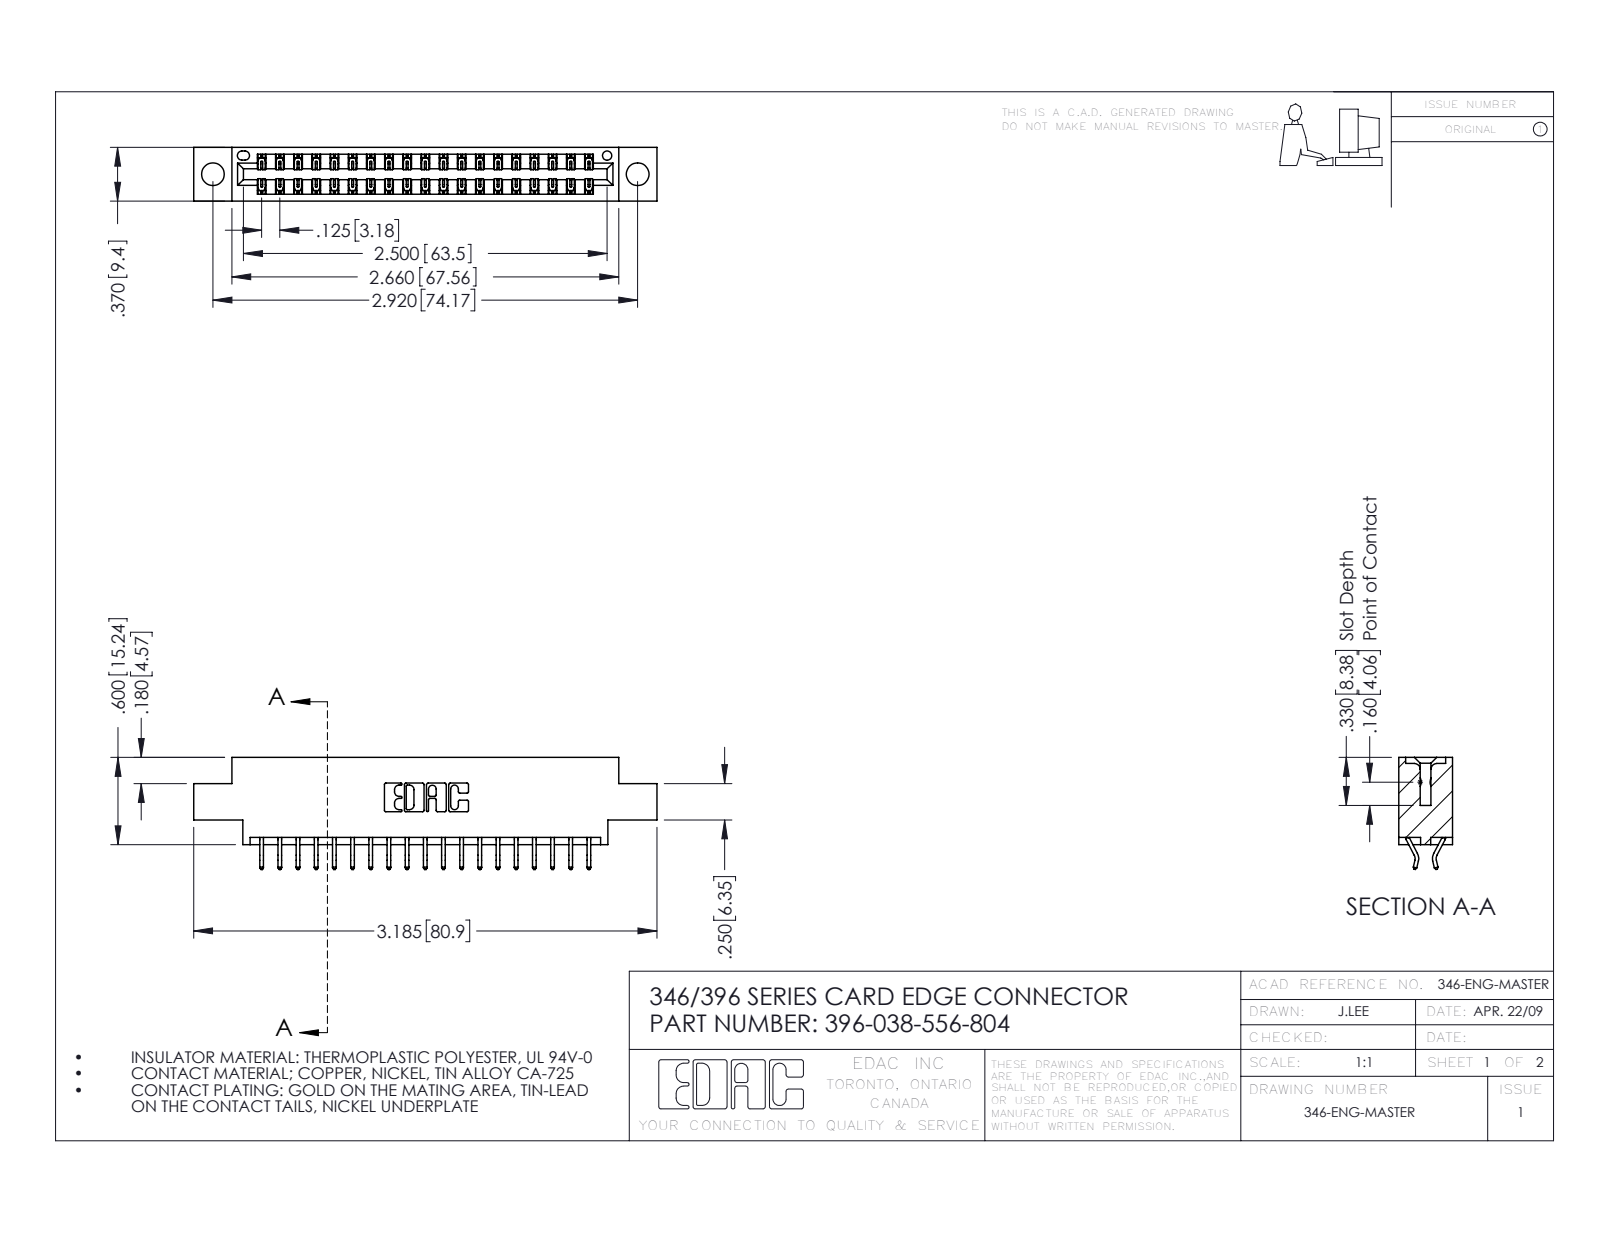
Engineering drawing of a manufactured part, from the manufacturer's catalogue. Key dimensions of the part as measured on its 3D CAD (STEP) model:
Part name (STEP PRODUCT): 396-038-556-804; 346 Part_0.170 Offset - 0.156 Dia-TH; 345-292-001_556 Tail
STEP written by: SolidWorks 2016 (CONFIG_CONTROL_DESIGN)
Units: inches
Bodies: 39 solids, 2330 faces (1562 planar, 768 cylindrical, 0 other)
Overall size (bounding box): 3.185 × 0.77 × 0.37
Volume: 0.456 in³ · Surface area: 15.28 in²
Round holes (diameter × count): ⌀0.156 ×2, ⌀0.064 ×1
Partial cylindrical surfaces — rounded edges, fillets, slot ends (radius × count): R0.006 ×57, R0.01 ×22, R0.007 ×6, R0.031 ×6, R0.026 ×3, R0.01 ×2, R0.014 ×2, R0.022 ×2
Main face-to-face distances: 0.048, 0.322, 0.37, 0.25, 0.025, 0.072, 0.298, 0.275, 0.148, 0.222
Hole centre spacings: 0.246, 2.713, 2.92
